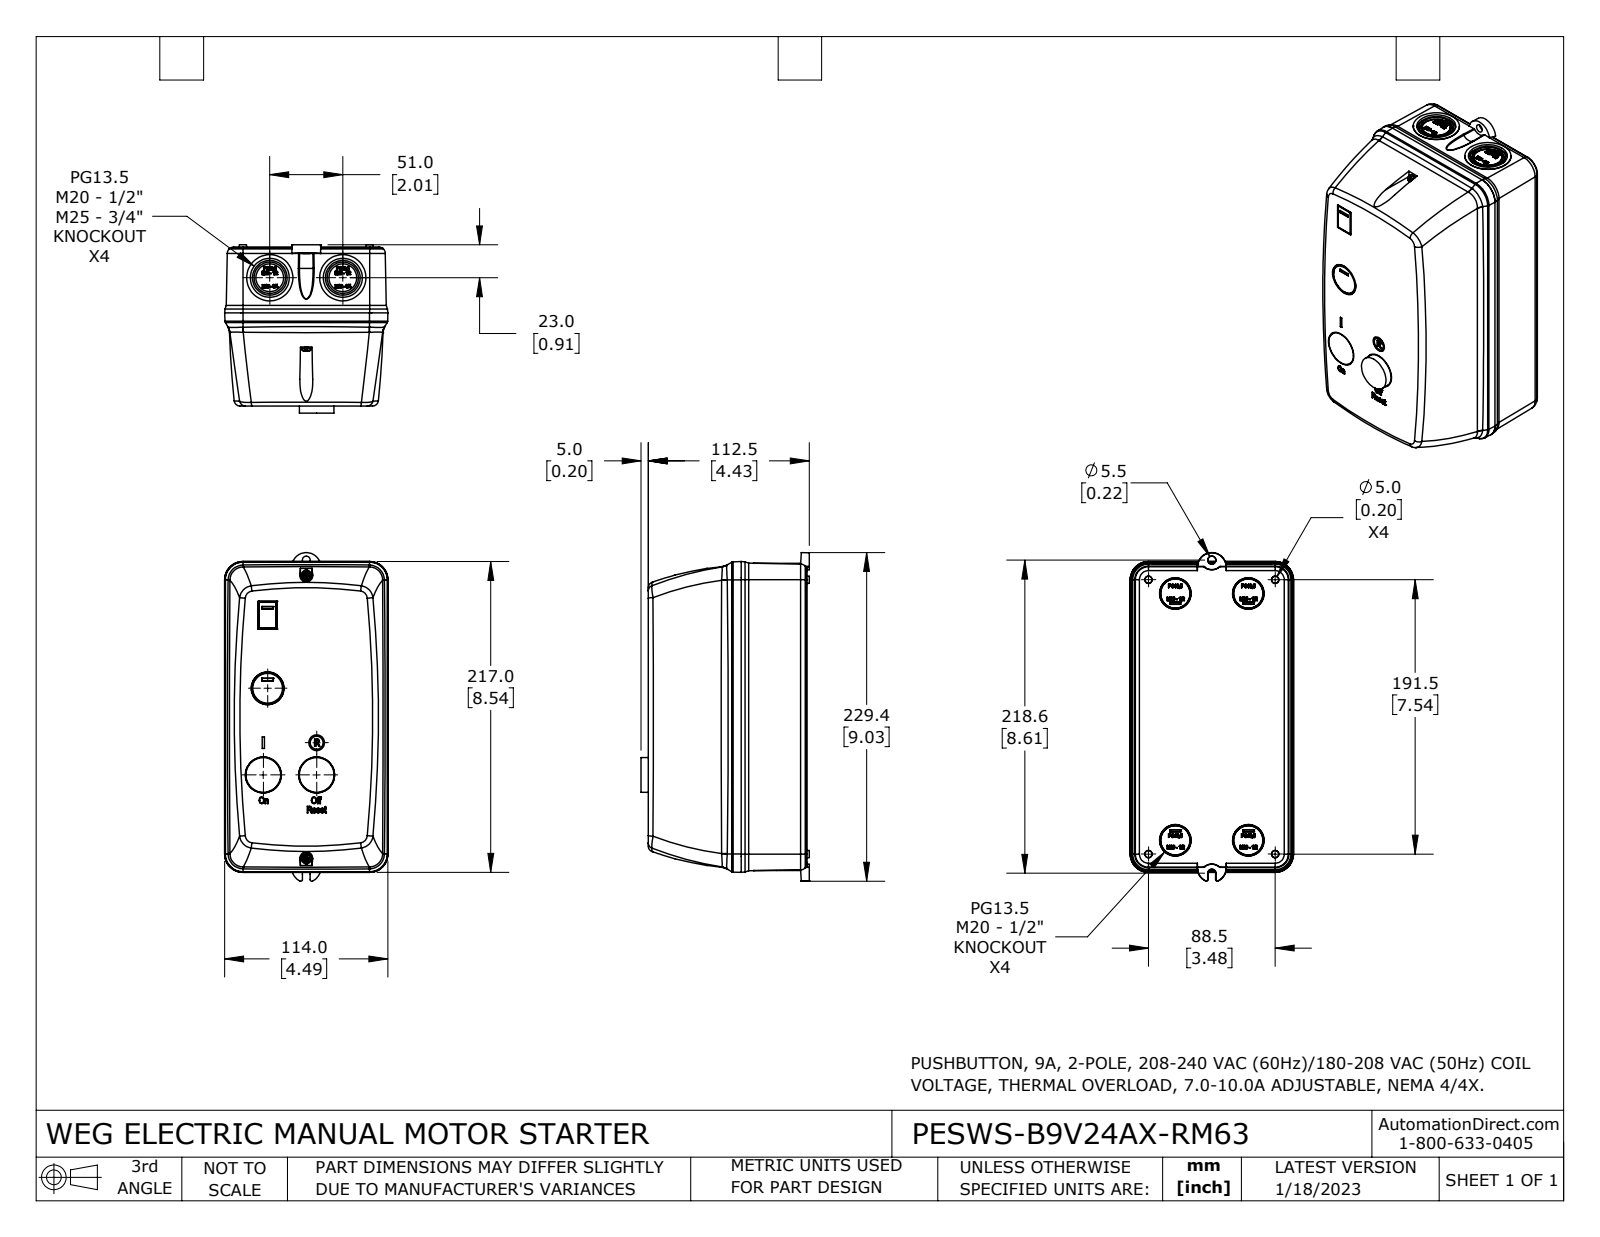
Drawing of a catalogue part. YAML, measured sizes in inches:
part_name: "PESWS-B9V24AX-RM63"
step_written_by: "SolidWorks 2021 (CONFIG_CONTROL_DESIGN)"
units: inches
bodies: {solids: 6, faces: 2195, planar: 1110, cylindrical: 92, other: 993}
overall_size: [9.033, 4.626, 4.489]
volume: 149.9
surface_area: 257.6
round_holes:
  - {diameter: 0.173, count: 2}
  - {diameter: 0.863, count: 2}
  - {diameter: 1.072, count: 2}
  - {diameter: 0.217, count: 1}
  - {diameter: 0.433, count: 1}
round_bosses_or_shafts:
  - {diameter: 1.27, count: 2}
  - {diameter: 0.955, count: 2}
  - {diameter: 0.953, count: 2}
  - {diameter: 0.763, count: 2}
  - {diameter: 0.276, count: 2}
  - {diameter: 0.118, count: 2}
  - {diameter: 0.354, count: 1}
partial_cylinders:
  - {radius: 0.079, count: 4}
  - {radius: 0.181, count: 4}
  - {radius: 0.376, count: 4}
  - {radius: 0.257, count: 2}
  - {radius: 0.297, count: 2}
  - {radius: 0.082, count: 1}
  - {radius: 0.085, count: 1}
  - {radius: 0.108, count: 1}
face_to_face_distances: [1.811, 2.559, 4.37, 0.02, 4.35, 1.791, 4.331, 0.039, 4.311, 2.52]
hole_center_spacings: [0.413, 2.008, 3.202, 4.615, 5.028, 7.795, 8.209]
